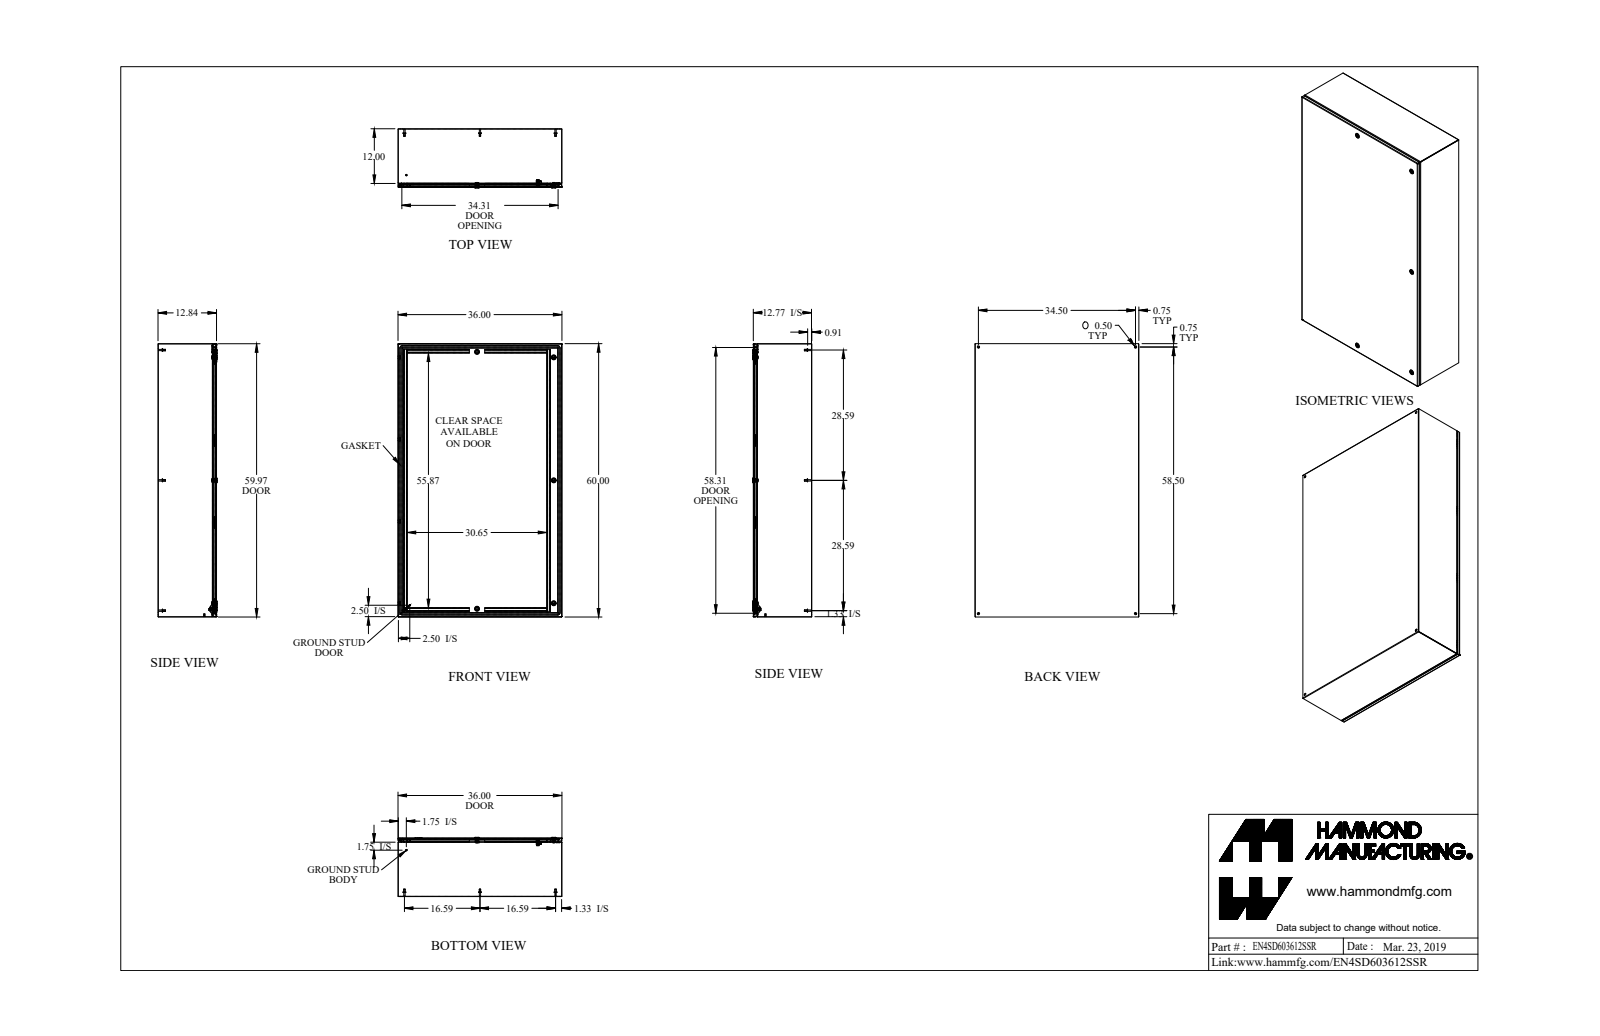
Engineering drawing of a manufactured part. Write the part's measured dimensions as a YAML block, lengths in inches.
part_name: "EN4SD603612SSR"
step_written_by: "SolidWorks 2018 (AUTOMOTIVE_DESIGN)"
units: inches
bodies: {solids: 66, faces: 1711, planar: 896, cylindrical: 546, other: 269}
overall_size: [60, 36, 13.002]
volume: 545
surface_area: 15475
round_holes:
  - {diameter: 0.5, count: 9}
  - {diameter: 0.197, count: 5}
  - {diameter: 0.387, count: 5}
  - {diameter: 0.63, count: 5}
  - {diameter: 0.768, count: 5}
  - {diameter: 0.172, count: 1}
  - {diameter: 0.196, count: 1}
  - {diameter: 0.24, count: 1}
  - {diameter: 0.242, count: 1}
  - {diameter: 0.275, count: 1}
  - {diameter: 0.375, count: 1}
round_bosses_or_shafts:
  - {diameter: 0.625, count: 11}
  - {diameter: 0.313, count: 10}
  - {diameter: 0.275, count: 8}
  - {diameter: 1.1, count: 5}
  - {diameter: 0.236, count: 5}
  - {diameter: 0.785, count: 3}
  - {diameter: 0.625, count: 3}
  - {diameter: 0.525, count: 3}
partial_cylinders:
  - {radius: 0.043, count: 24}
  - {radius: 0.036, count: 18}
  - {radius: 0.108, count: 18}
  - {radius: 0.062, count: 17}
  - {radius: 0.094, count: 10}
  - {radius: 0.125, count: 10}
  - {radius: 0.016, count: 9}
  - {radius: 0.006, count: 8}
face_to_face_distances: [0.072, 12.77, 12.698, 12.842, 59.928, 0.072, 35.856, 35.928, 35.928, 36]
hole_center_spacings: [2.501, 16.635, 16.881, 17.931, 26.985, 29.269, 32.835, 33.516]
